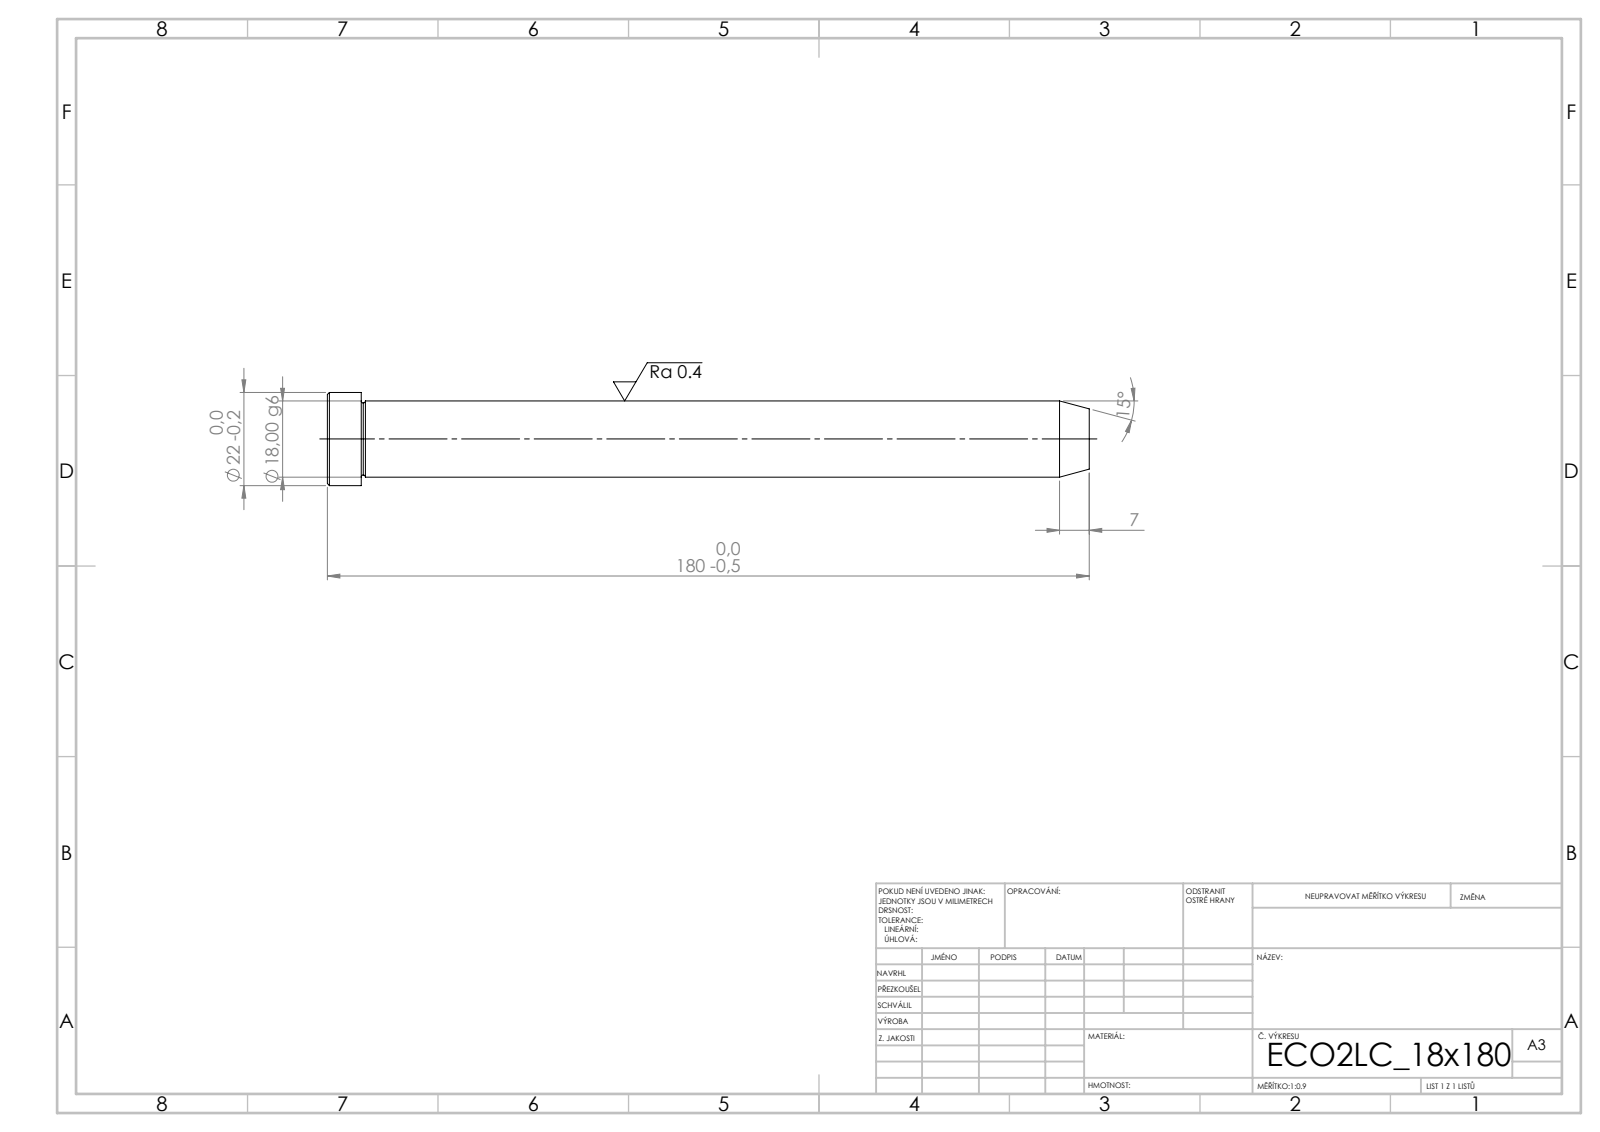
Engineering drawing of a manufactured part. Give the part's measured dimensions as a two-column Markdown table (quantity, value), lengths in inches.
| quantity | value |
| --- | --- |
| STEP written by | SolidWorks 2019 (CONFIG_CONTROL_DESIGN) |
| units | inches |
| bodies | 1 solid, 15 faces (3 planar, 4 cylindrical, 8 other) |
| overall size | 7.087 × 0.866 × 0.866 |
| volume | 2.834 in³ |
| surface area | 16.93 in² |
| round bosses / shafts (diameter × count) | 0.866 × 1, 0.709 × 1 |
| main face-to-face distances | 7.087, 6.772, 0.315 |
